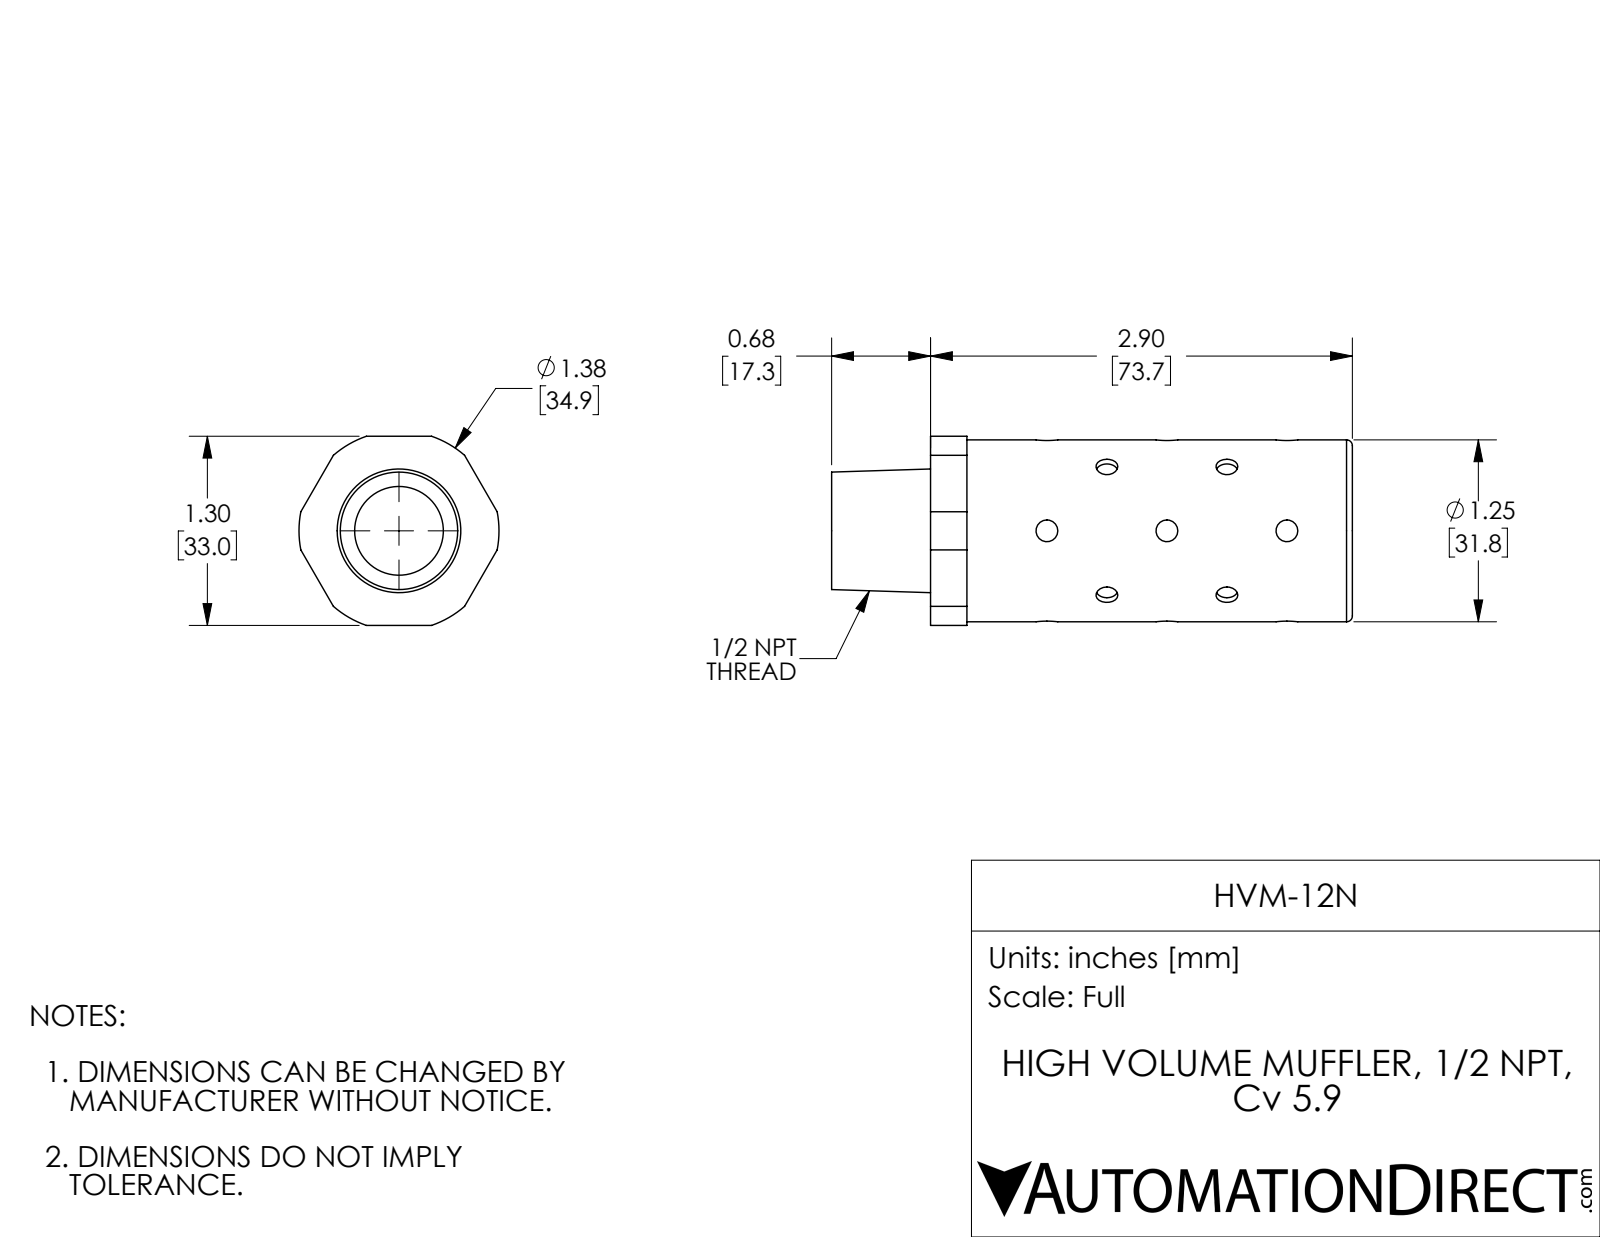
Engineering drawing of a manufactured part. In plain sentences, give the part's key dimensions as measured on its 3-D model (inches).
The part is named "HVM-12N". Its 3-D file was written by "SolidWorks 2017 (AUTOMOTIVE_DESIGN)". It is 1 solid with 86 faces: 31 planar, 51 cylindrical and 4 other. Overall it measures 3.58 by 1.375 by 1.3 inches. Its volume is 2.981 cubic inches and its surface area 22.79 square inches. Round holes: 10 of diameter 0.15, 1 of diameter 0.61. Round bosses or shafts: 1 of diameter 1.25. Partial cylindrical surfaces (rounded edges, fillets, slot ends): 1 of radius 0.687. The main face-to-face distances are 2.9, 0.25, 2.65, 1.3, 0.68, 3.33, 3.58, 0.93, 2.4, 0.075. The hole center spacings are 0.825, 0.825, 1.65.
